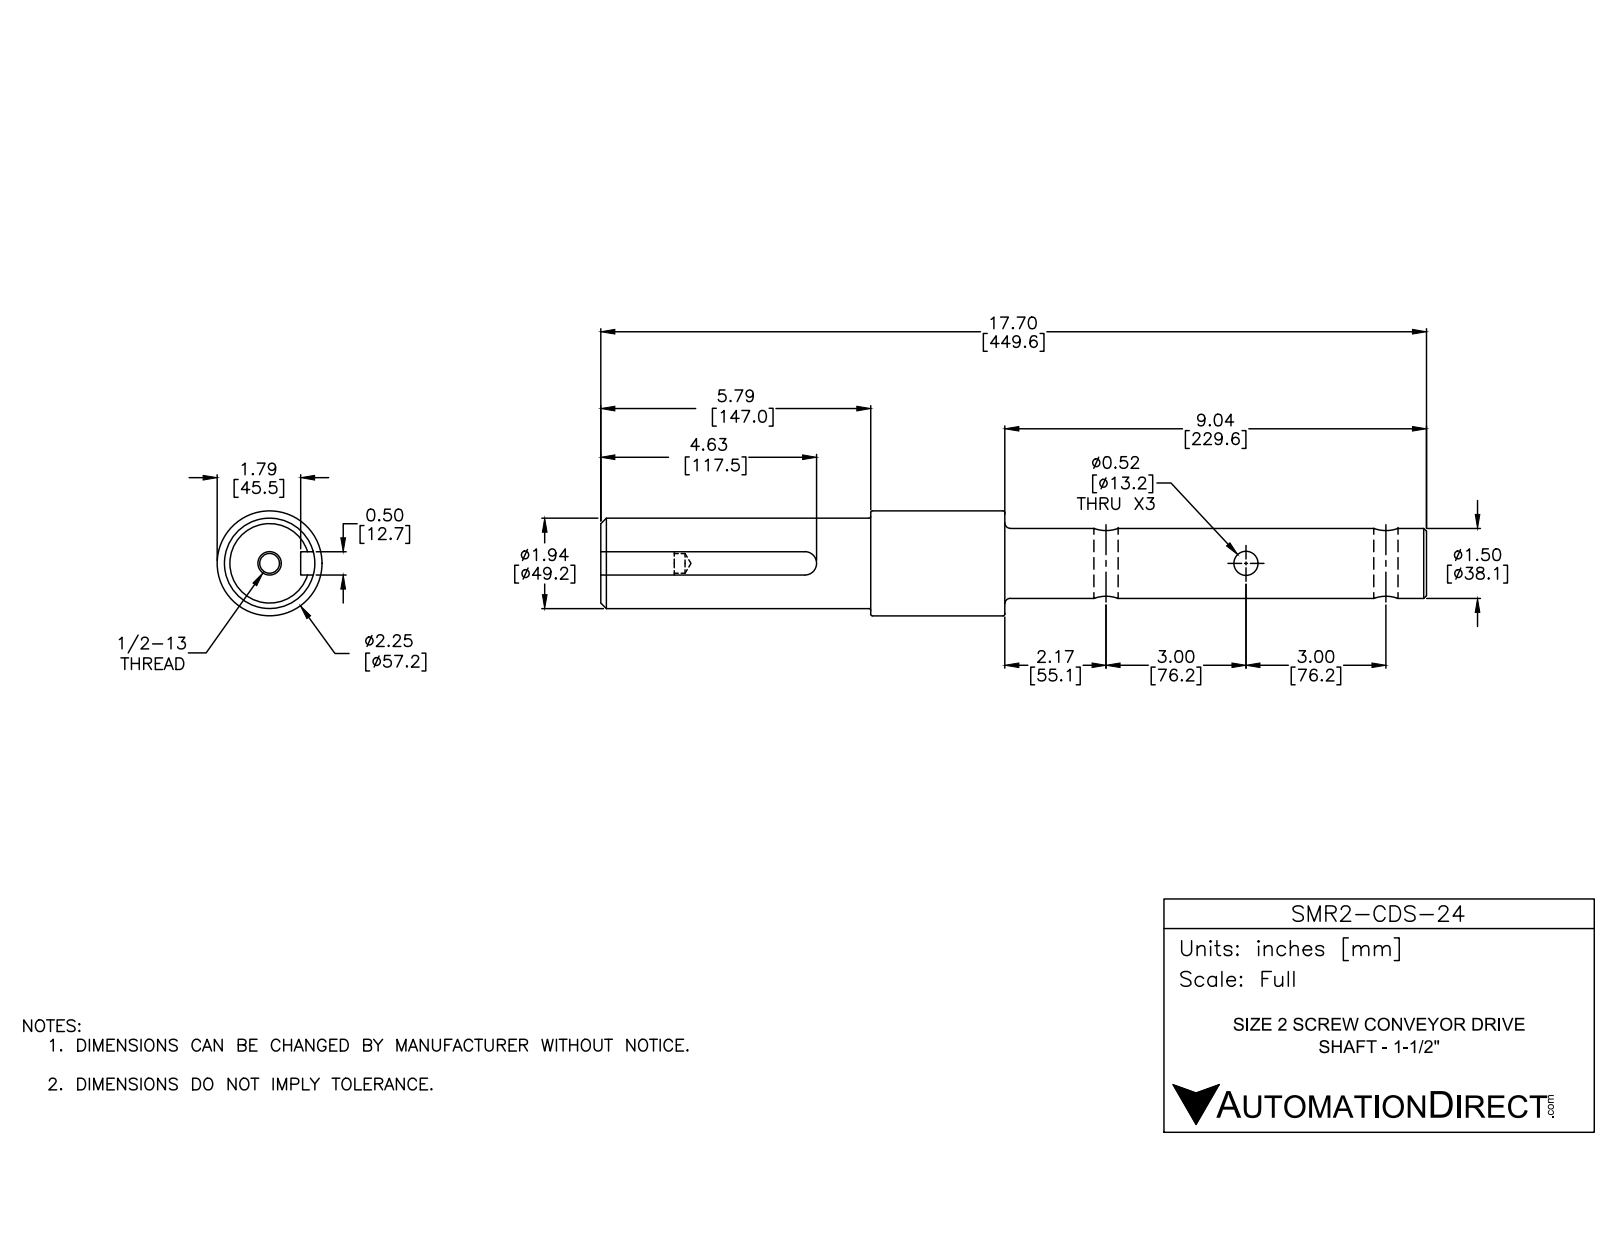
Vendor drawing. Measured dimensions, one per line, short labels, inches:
name: SMR2-CDS-24
written by: SolidWorks 2016 (AUTOMOTIVE_DESIGN)
unit: in
bodies: 1 solid, 40 faces (8 planar, 18 cylindrical, 14 other)
size: 17.701 × 2.25 × 2.25
volume: 42.47 in³; area: 116 in²
holes: 3× ⌀0.52, 1× ⌀0.422, 1× ⌀0.5
bosses: 1× ⌀2.25, 1× ⌀1.937, 1× ⌀1.5
rounds: 1× R0.25
face distances: 17.701, 8.661, 9.039, 0.5, 5.787, 2.874, 11.913, 1.575, 4.213, 7.087
hole spacings: 6
